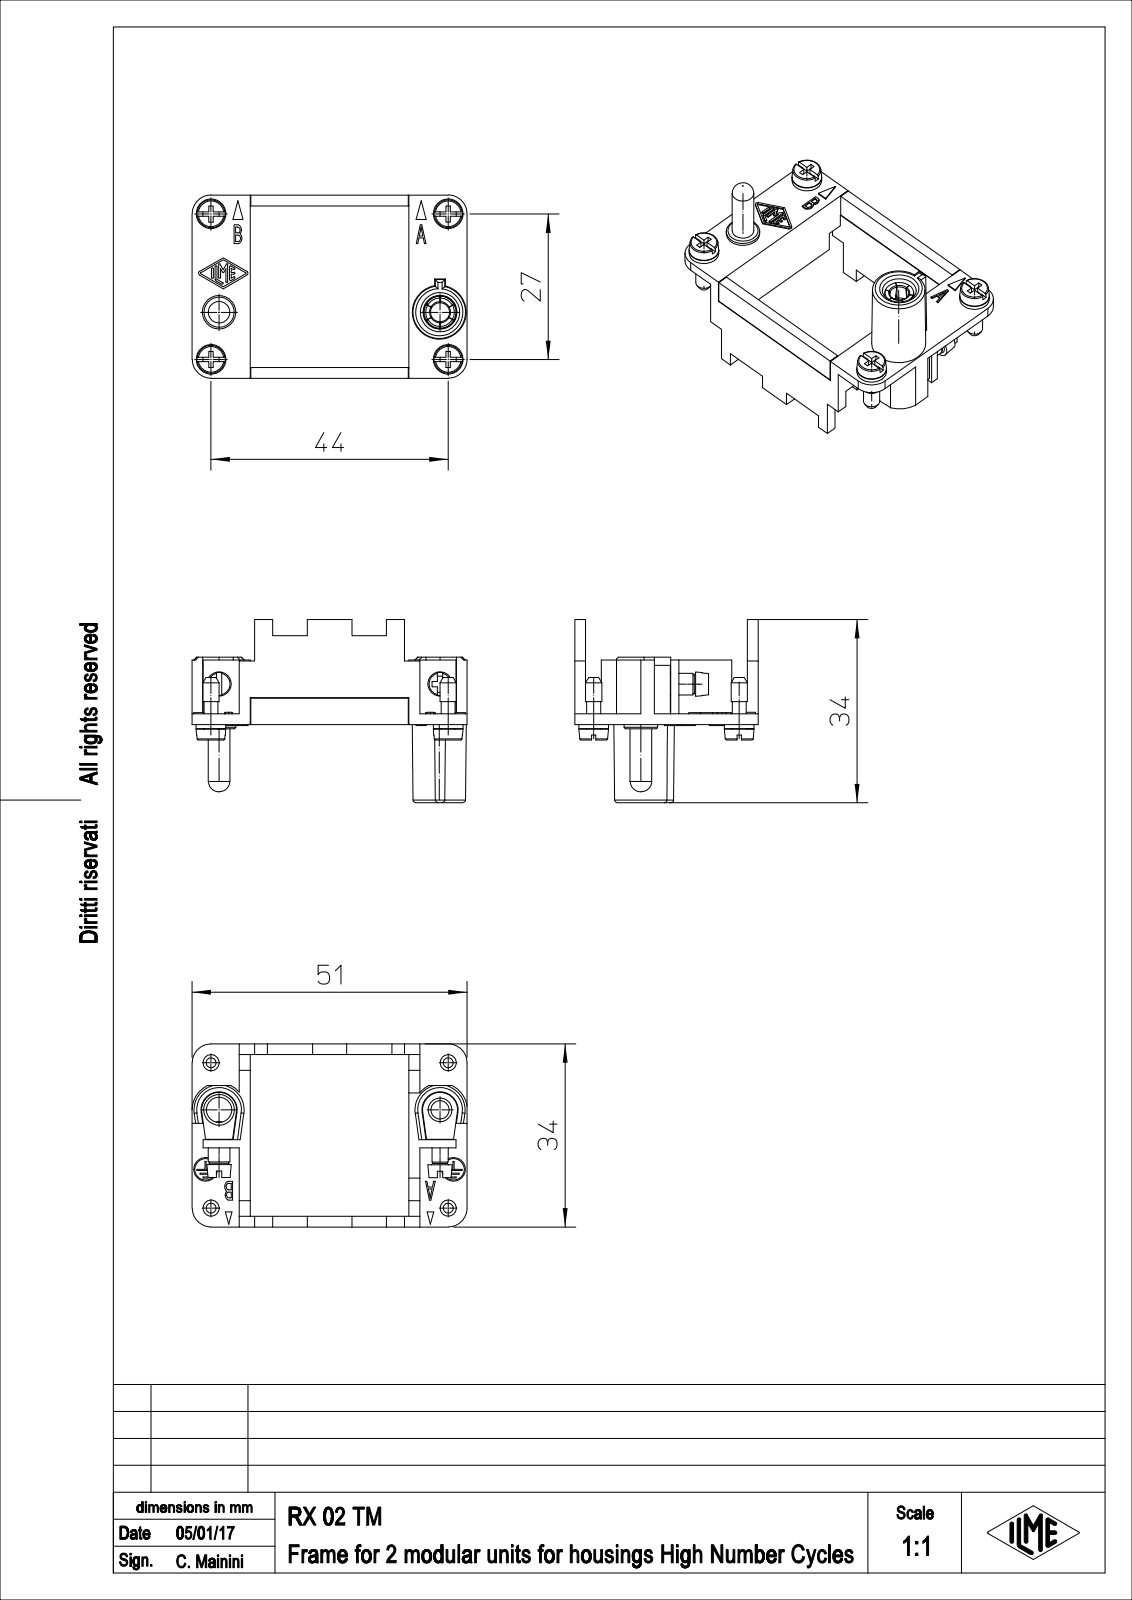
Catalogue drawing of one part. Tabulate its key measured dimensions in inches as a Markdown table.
| quantity | value |
| --- | --- |
| part name | RX_02_TM |
| STEP written by | PTC Creo Elements/Direct Modeling 19.0E 27-Jun-2016 (C) Parametric Technology GmbH (AUTOMOTIVE_DESIGN) |
| units | inches |
| bodies | 1 solid, 627 faces (411 planar, 104 cylindrical, 112 other) |
| overall size | 2.008 × 1.339 × 1.339 |
| volume | 0.469 in³ |
| surface area | 14.44 in² |
| round holes (diameter × count) | 0.157 × 2, 0.098 × 1, 0.13 × 1, 0.134 × 1, 0.165 × 1, 0.185 × 1, 0.248 × 1 |
| round bosses / shafts (diameter × count) | 0.118 × 5, 0.217 × 4, 0.102 × 4, 0.173 × 2, 0.157 × 2, 0.244 × 1, 0.236 × 1, 0.138 × 1 |
| partial cylindrical surfaces (radius × count) | 0.007 × 11, 0.138 × 4, 0.02 × 3, 0.005 × 2, 0.016 × 2, 0.128 × 2, 0.132 × 2, 0.197 × 2 |
| main face-to-face distances | 0.079, 1.26, 1.339, 1.181, 0.081, 1.238, 1.157, 0.112, 0.344, 1.583 |
| hole center spacings | 0.446, 1.614, 1.767, 1.767, 1.811 |
